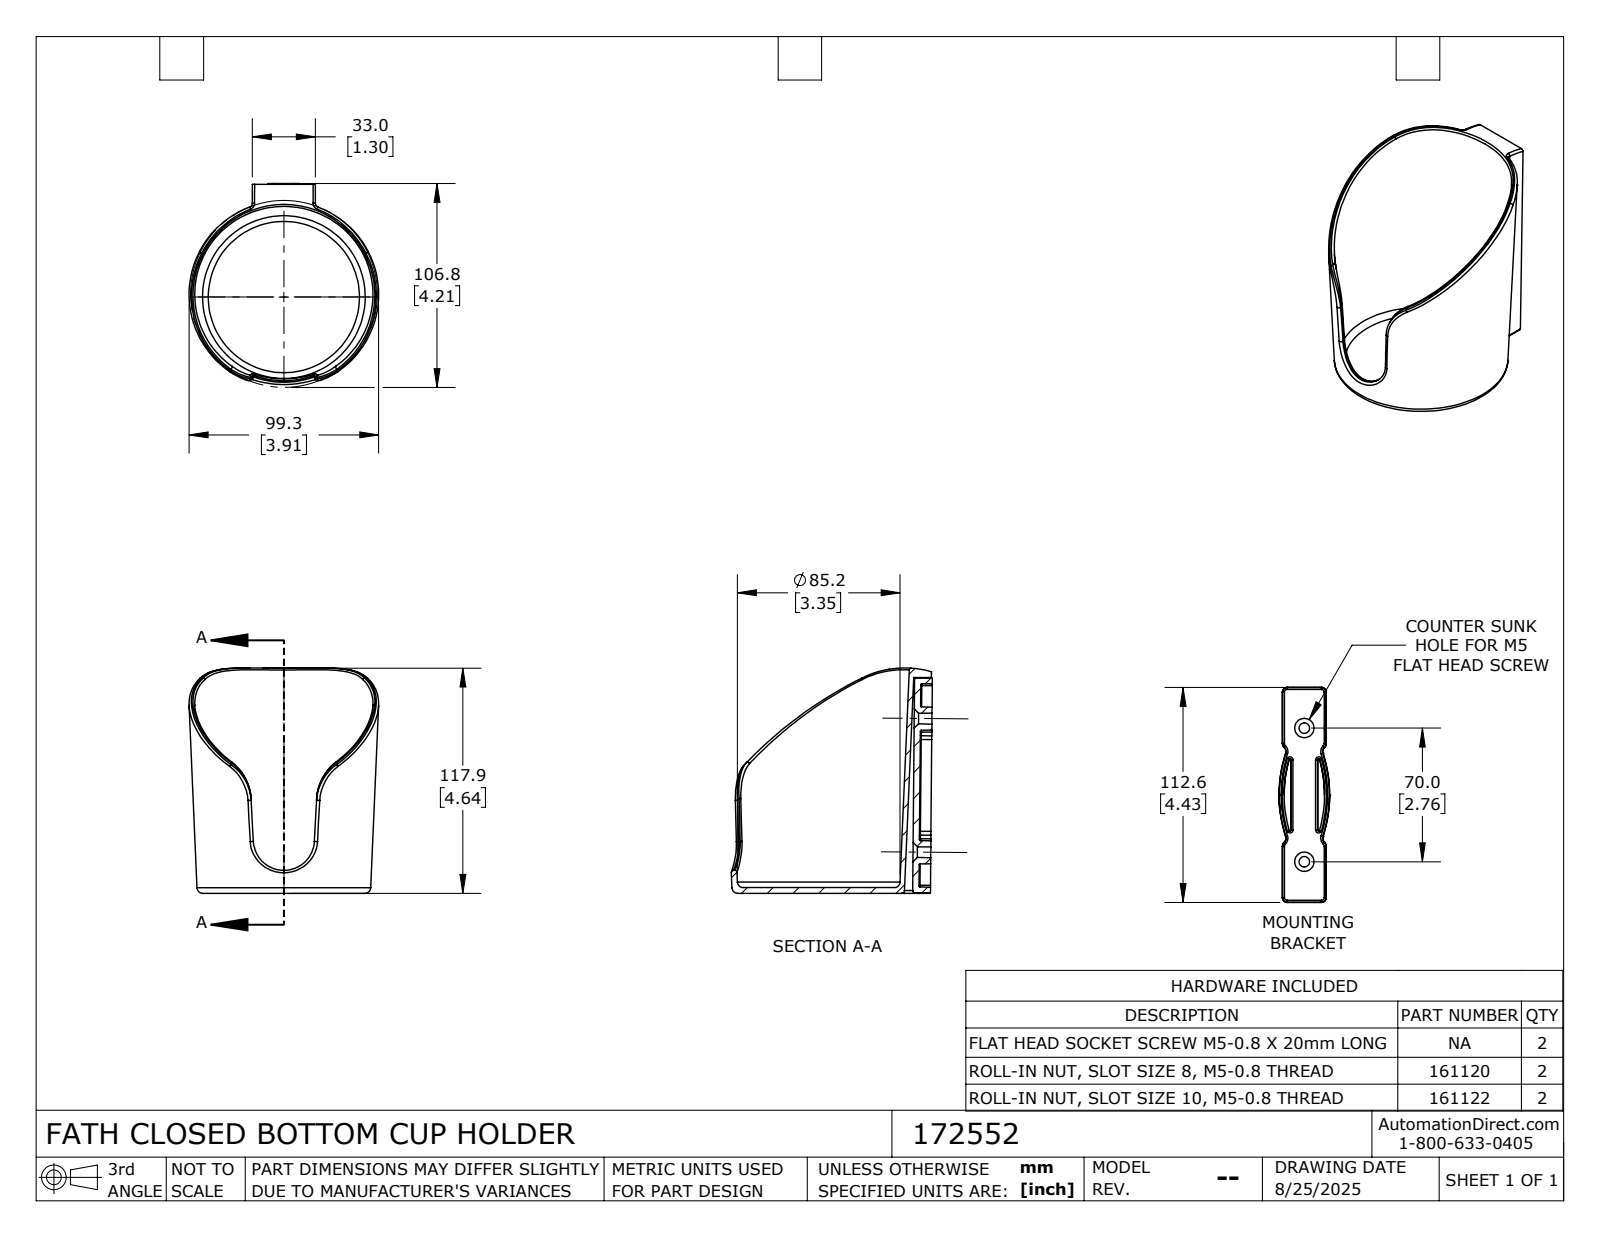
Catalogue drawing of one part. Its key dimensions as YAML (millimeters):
part_name: "172552"
step_written_by: "SolidWorks 2024 (CONFIG_CONTROL_DESIGN)"
units: millimeters
bodies: {solids: 2, faces: 282, planar: 58, cylindrical: 47, other: 177}
overall_size: [119.98, 105.3, 99.32]
volume: 123416
surface_area: 79509
partial_cylinders:
  - {radius: 0.5, count: 8}
  - {radius: 1, count: 8}
  - {radius: 1.5, count: 6}
  - {radius: 3, count: 4}
  - {radius: 2, count: 2}
  - {radius: 10, count: 2}
  - {radius: 67.8, count: 2}
  - {radius: 70.5, count: 2}
face_to_face_distances: [3, 8.81, 27.75, 24.75, 0.5, 9.31, 1.5, 12.38, 6.31, 5.81]
